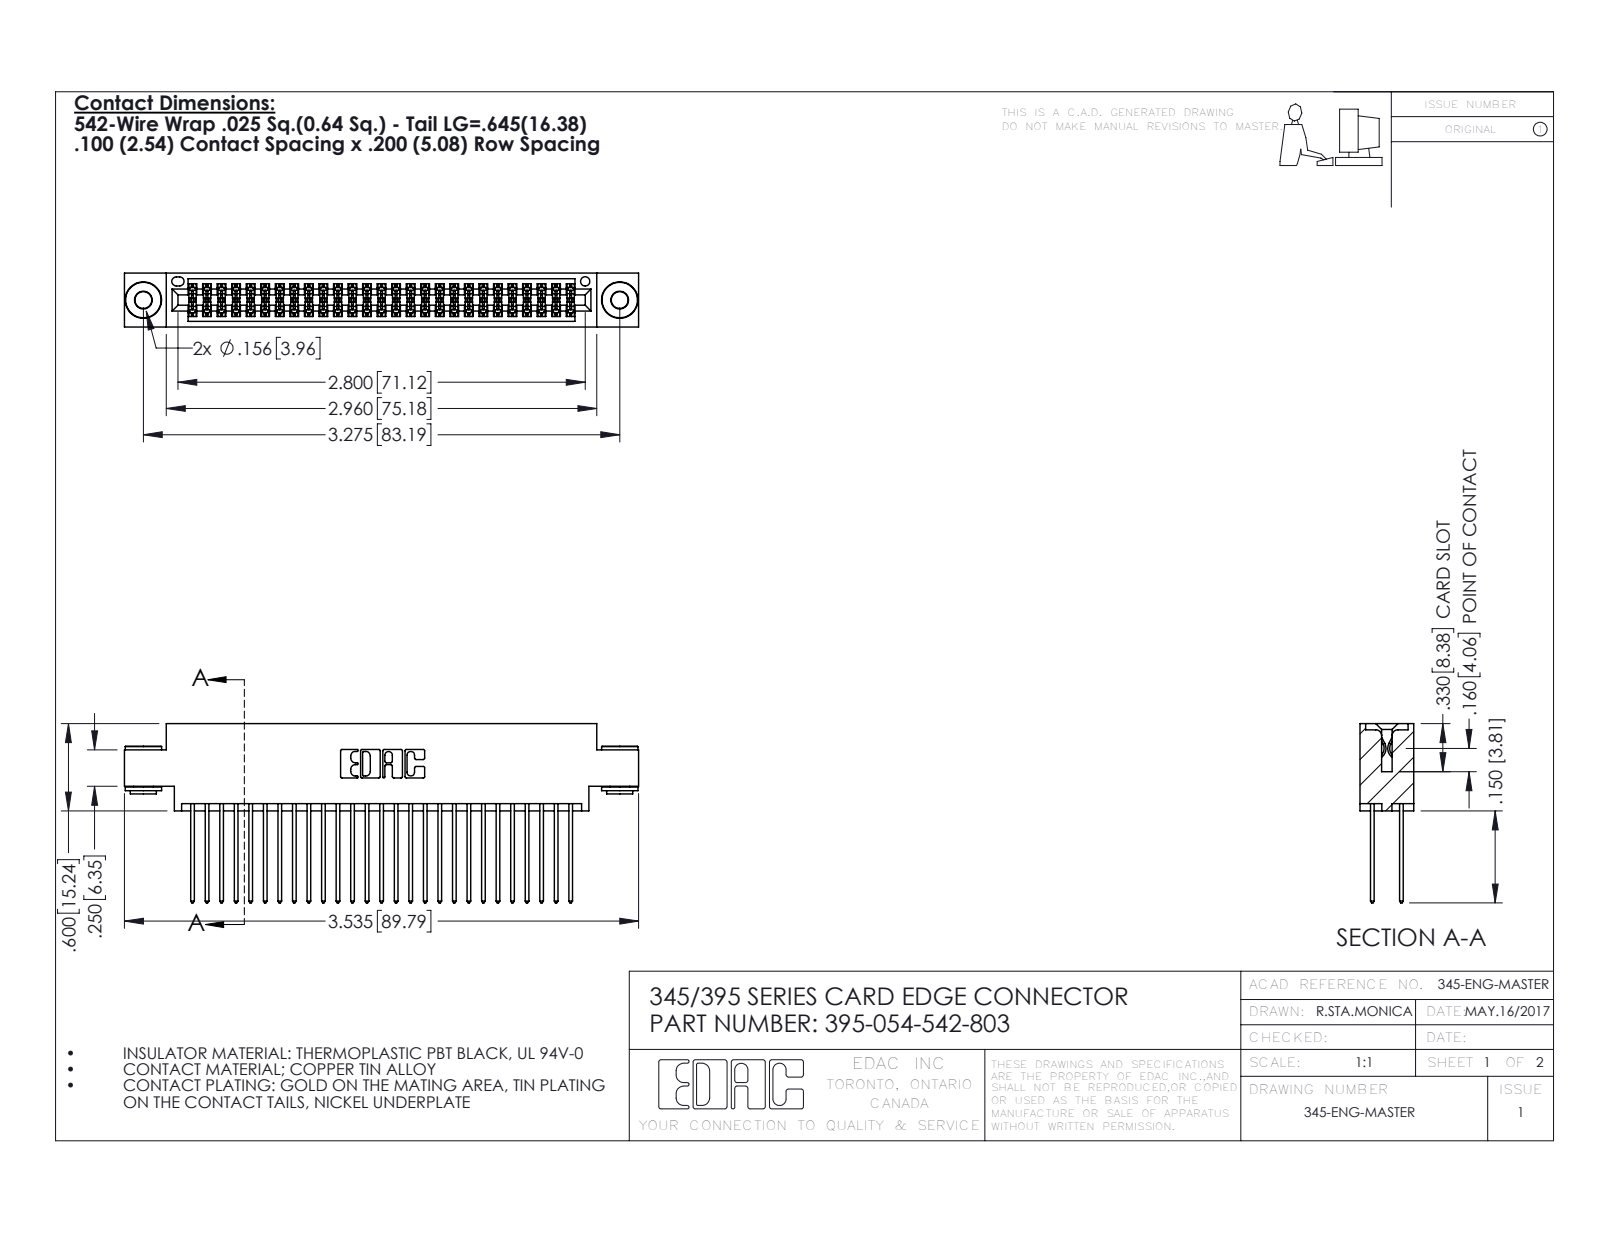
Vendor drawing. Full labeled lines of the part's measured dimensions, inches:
Part name (STEP PRODUCT): 345-292-001_345-293-142; 345-250-002_345-250-002-102; 395-054-542-803; 345 Part_0.170 Offset - 0.156 Dia-TH
STEP written by: SolidWorks 2016 (CONFIG_CONTROL_DESIGN)
Units: inches
Bodies: 57 solids, 2868 faces (1876 planar, 984 cylindrical, 8 other)
Overall size (bounding box): 3.535 × 1.232 × 0.37
Volume: 0.533 in³ · Surface area: 21.94 in²
Round holes (diameter × count): ⌀0.116 ×2, ⌀0.156 ×2, ⌀0.064 ×1
Round bosses / shafts (diameter × count): ⌀0.25 ×2, ⌀0.18 ×2, ⌀0.136 ×2
Partial cylindrical surfaces — rounded edges, fillets, slot ends (radius × count): R0.006 ×81, R0.01 ×54, R0.01 ×22, R0.007 ×6, R0.031 ×6, R0.026 ×3, R0.014 ×2, R0.019 ×2
Main face-to-face distances: 0.072, 0.298, 0.2, 0.098, 0.272, 0.025, 0.37, 0.225, 0.175, 0.1
Hole centre spacings: 0.27, 3.04, 3.275
